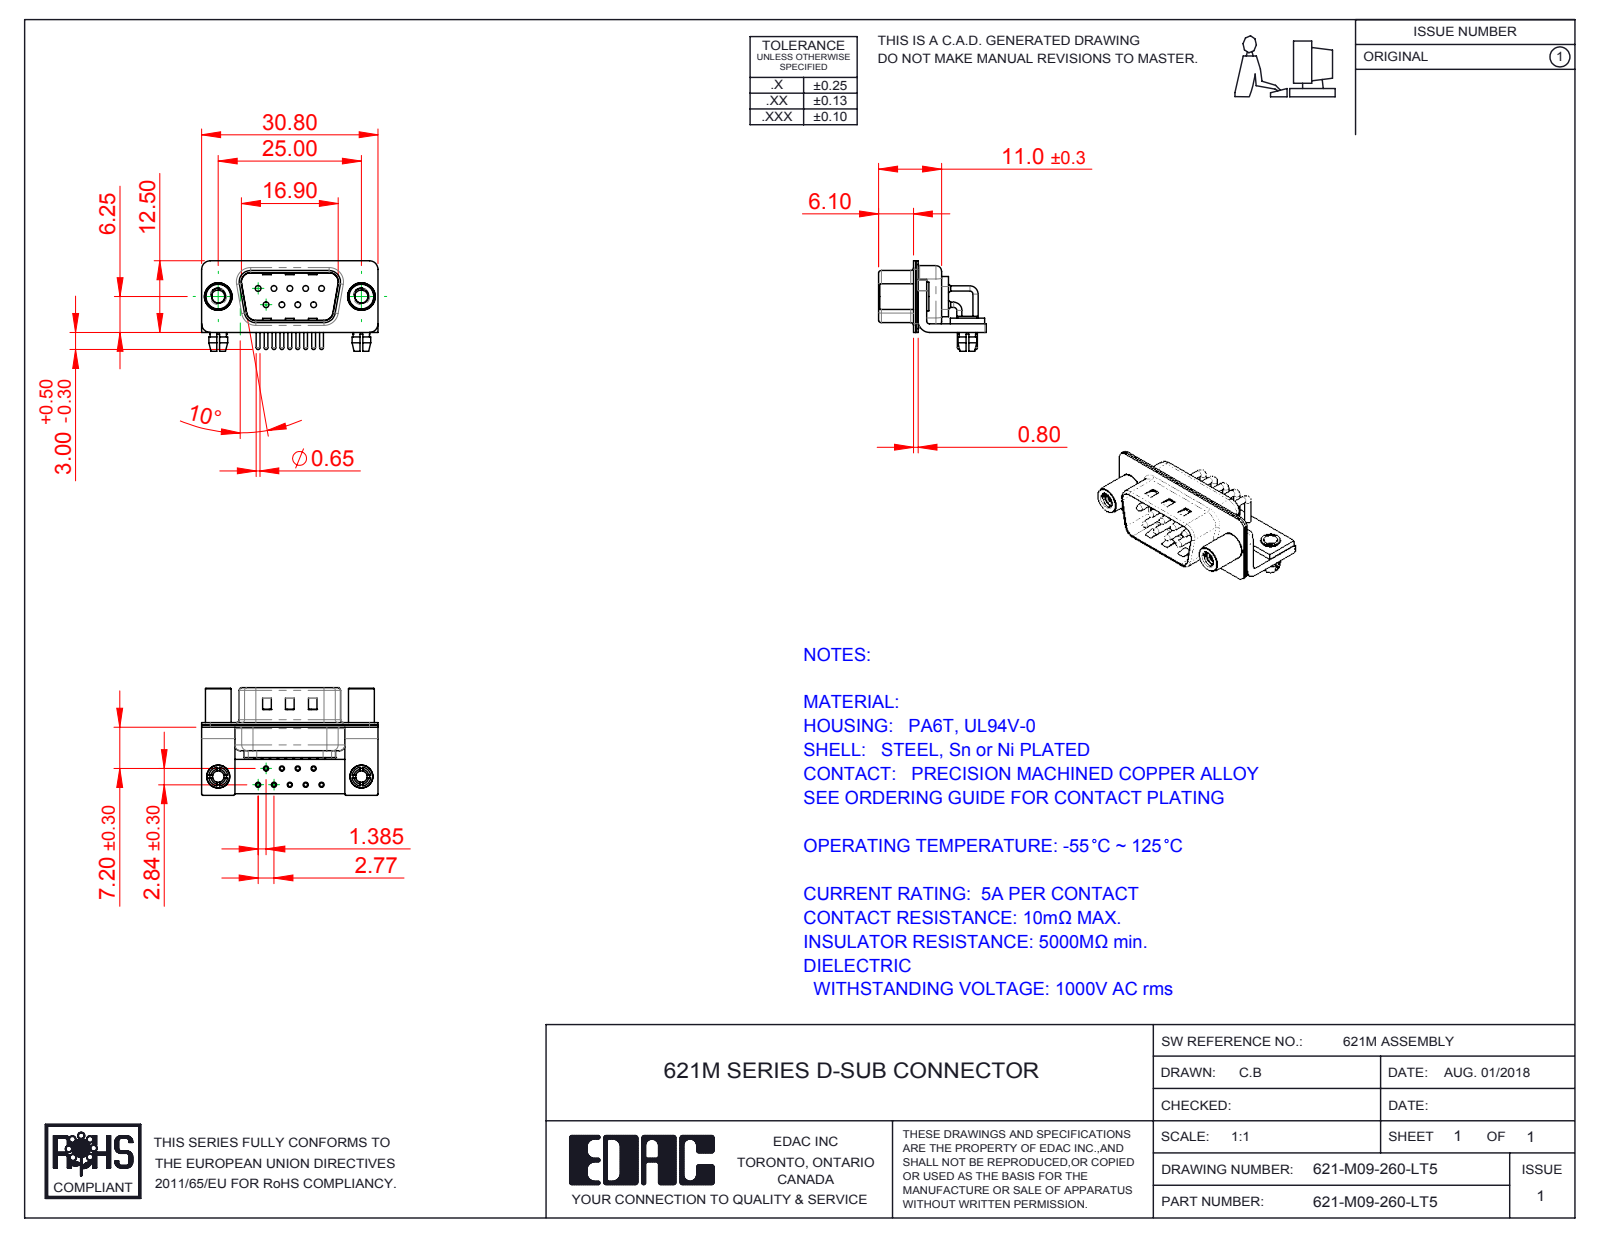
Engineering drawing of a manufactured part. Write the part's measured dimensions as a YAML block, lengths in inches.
part_name: "621M 4-40 Threaded Standoff; 621M Stabilizer Bracket; 621M Contact Row 2; 621M Contact Row 1 (+6 more)"
step_written_by: "SolidWorks 2016 (CONFIG_CONTROL_DESIGN)"
units: inches
bodies: {solids: 19, faces: 1504, planar: 759, cylindrical: 567, other: 178}
overall_size: [1.213, 0.74, 0.622]
volume: 0.118
surface_area: 8.333
round_holes:
  - {diameter: 0.079, count: 11}
  - {diameter: 0.035, count: 9}
  - {diameter: 0.039, count: 9}
  - {diameter: 0.067, count: 9}
  - {diameter: 0.089, count: 2}
  - {diameter: 0.098, count: 2}
  - {diameter: 0.126, count: 2}
  - {diameter: 0.157, count: 2}
  - {diameter: 0.189, count: 2}
round_bosses_or_shafts:
  - {diameter: 0.059, count: 9}
  - {diameter: 0.035, count: 9}
  - {diameter: 0.026, count: 9}
  - {diameter: 0.197, count: 2}
  - {diameter: 0.193, count: 2}
  - {diameter: 0.177, count: 2}
  - {diameter: 0.157, count: 2}
  - {diameter: 0.134, count: 2}
partial_cylinders:
  - {radius: 0.01, count: 16}
  - {radius: 0.059, count: 16}
  - {radius: 0.079, count: 13}
  - {radius: 0.02, count: 9}
  - {radius: 0.04, count: 9}
  - {radius: 0.063, count: 8}
  - {radius: 0.024, count: 4}
  - {radius: 0.026, count: 4}
face_to_face_distances: [0.016, 0.059, 0.031, 0.033, 0.049, 0.075, 0.039, 0.409, 0.376, 0.098]
hole_center_spacings: [0.124, 0.109, 0.218, 0.198, 0.198, 0.327, 0.294, 0.295]
